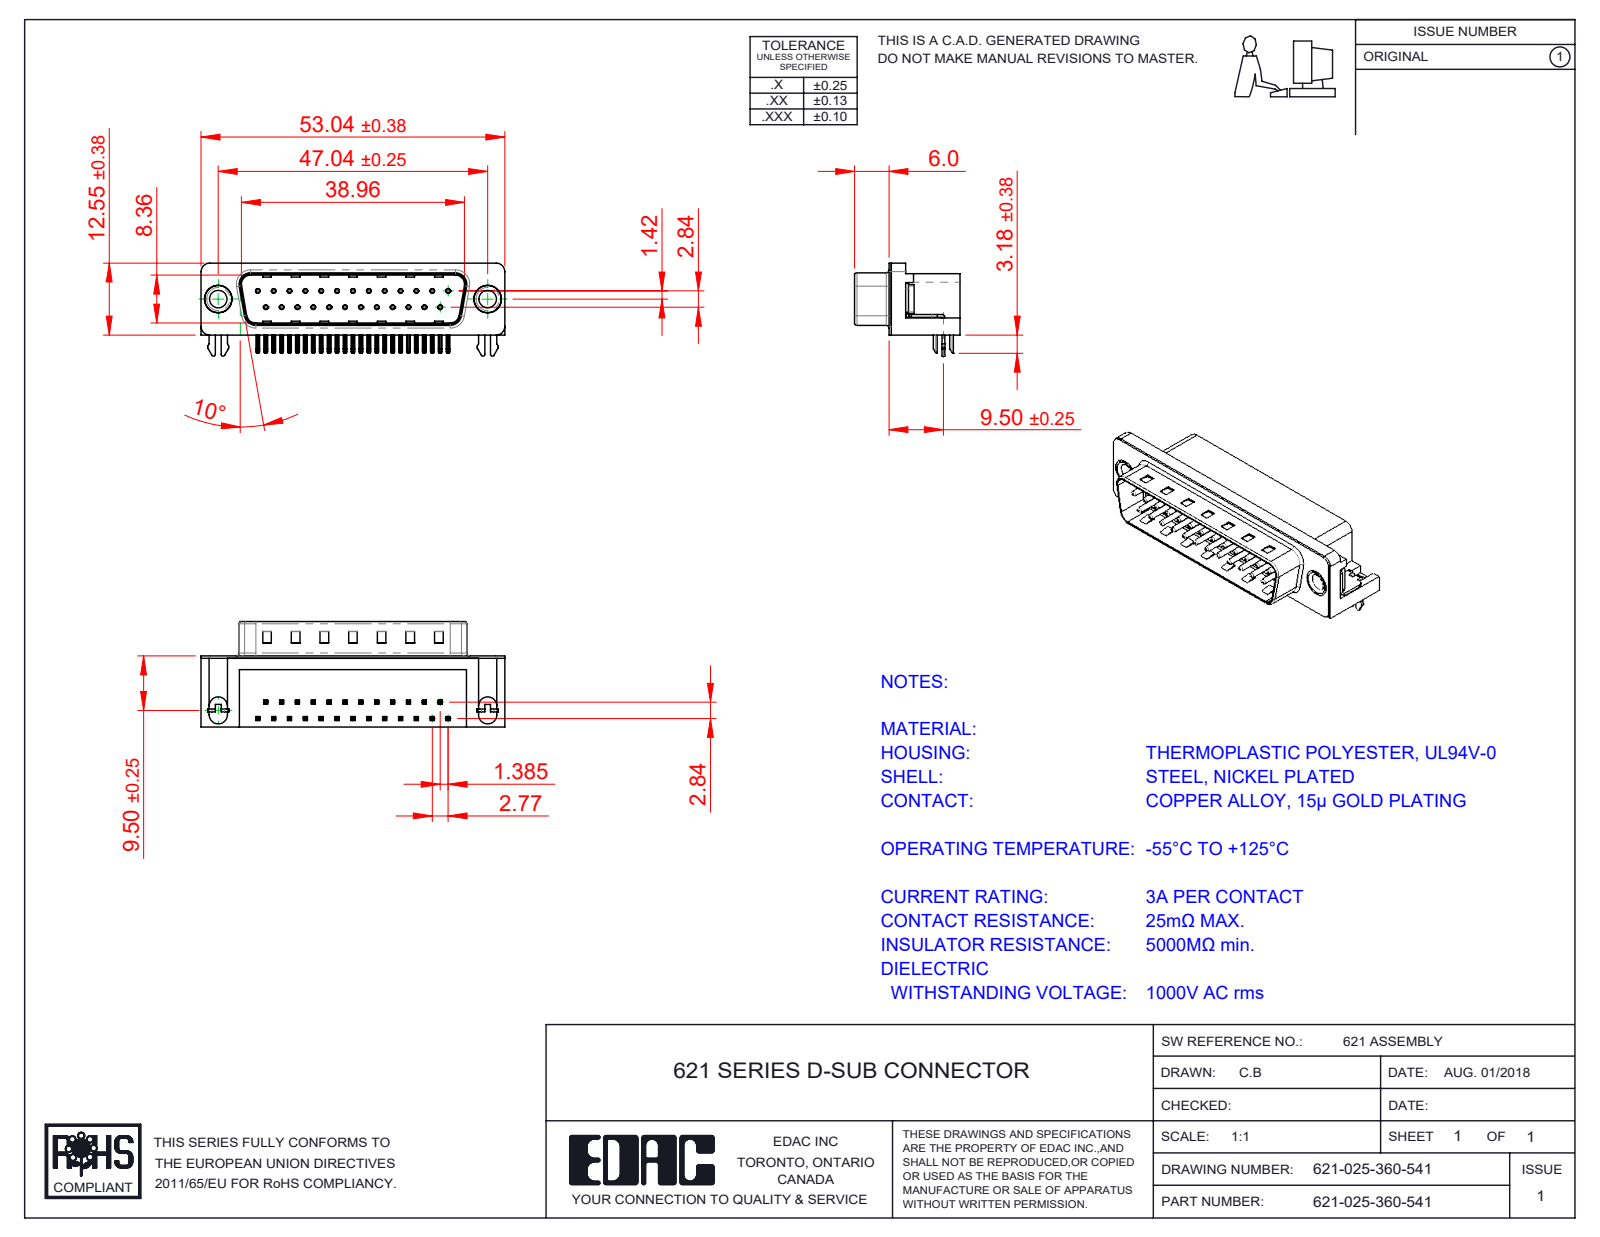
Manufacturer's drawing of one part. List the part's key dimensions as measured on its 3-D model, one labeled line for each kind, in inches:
Part name (STEP PRODUCT): 621 Thru Hole Rivet; 621 Shell_25 Socket; 621 Housing_25 Socket; 621 Contact Top (+3 more)
STEP written by: SolidWorks 2016 (CONFIG_CONTROL_DESIGN)
Units: inches
Bodies: 31 solids, 2343 faces (1447 planar, 647 cylindrical, 249 other)
Overall size (bounding box): 2.088 × 0.724 × 0.64
Volume: 0.387 in³ · Surface area: 11.99 in²
Round holes (diameter × count): ⌀0.014 ×25, ⌀0.031 ×25, ⌀0.079 ×2, ⌀0.12 ×2, ⌀0.157 ×2, ⌀0.189 ×2, ⌀0.197 ×2
Round bosses / shafts (diameter × count): ⌀0.03 ×25, ⌀0.193 ×2, ⌀0.187 ×2, ⌀0.152 ×2, ⌀0.118 ×2
Partial cylindrical surfaces — rounded edges, fillets, slot ends (radius × count): R0.01 ×112, R0.005 ×50, R0.039 ×16, R0.02 ×9, R0.063 ×8, R0.059 ×7, R0.035 ×4, R0.079 ×4
Main face-to-face distances: 0.016, 0.472, 0.407, 0.083, 0.345, 0.412, 0.067, 0.428, 0.488, 0.354
Hole centre spacings: 0.124, 0.109, 0.218, 0.327, 0.436, 0.545, 0.654, 0.198
